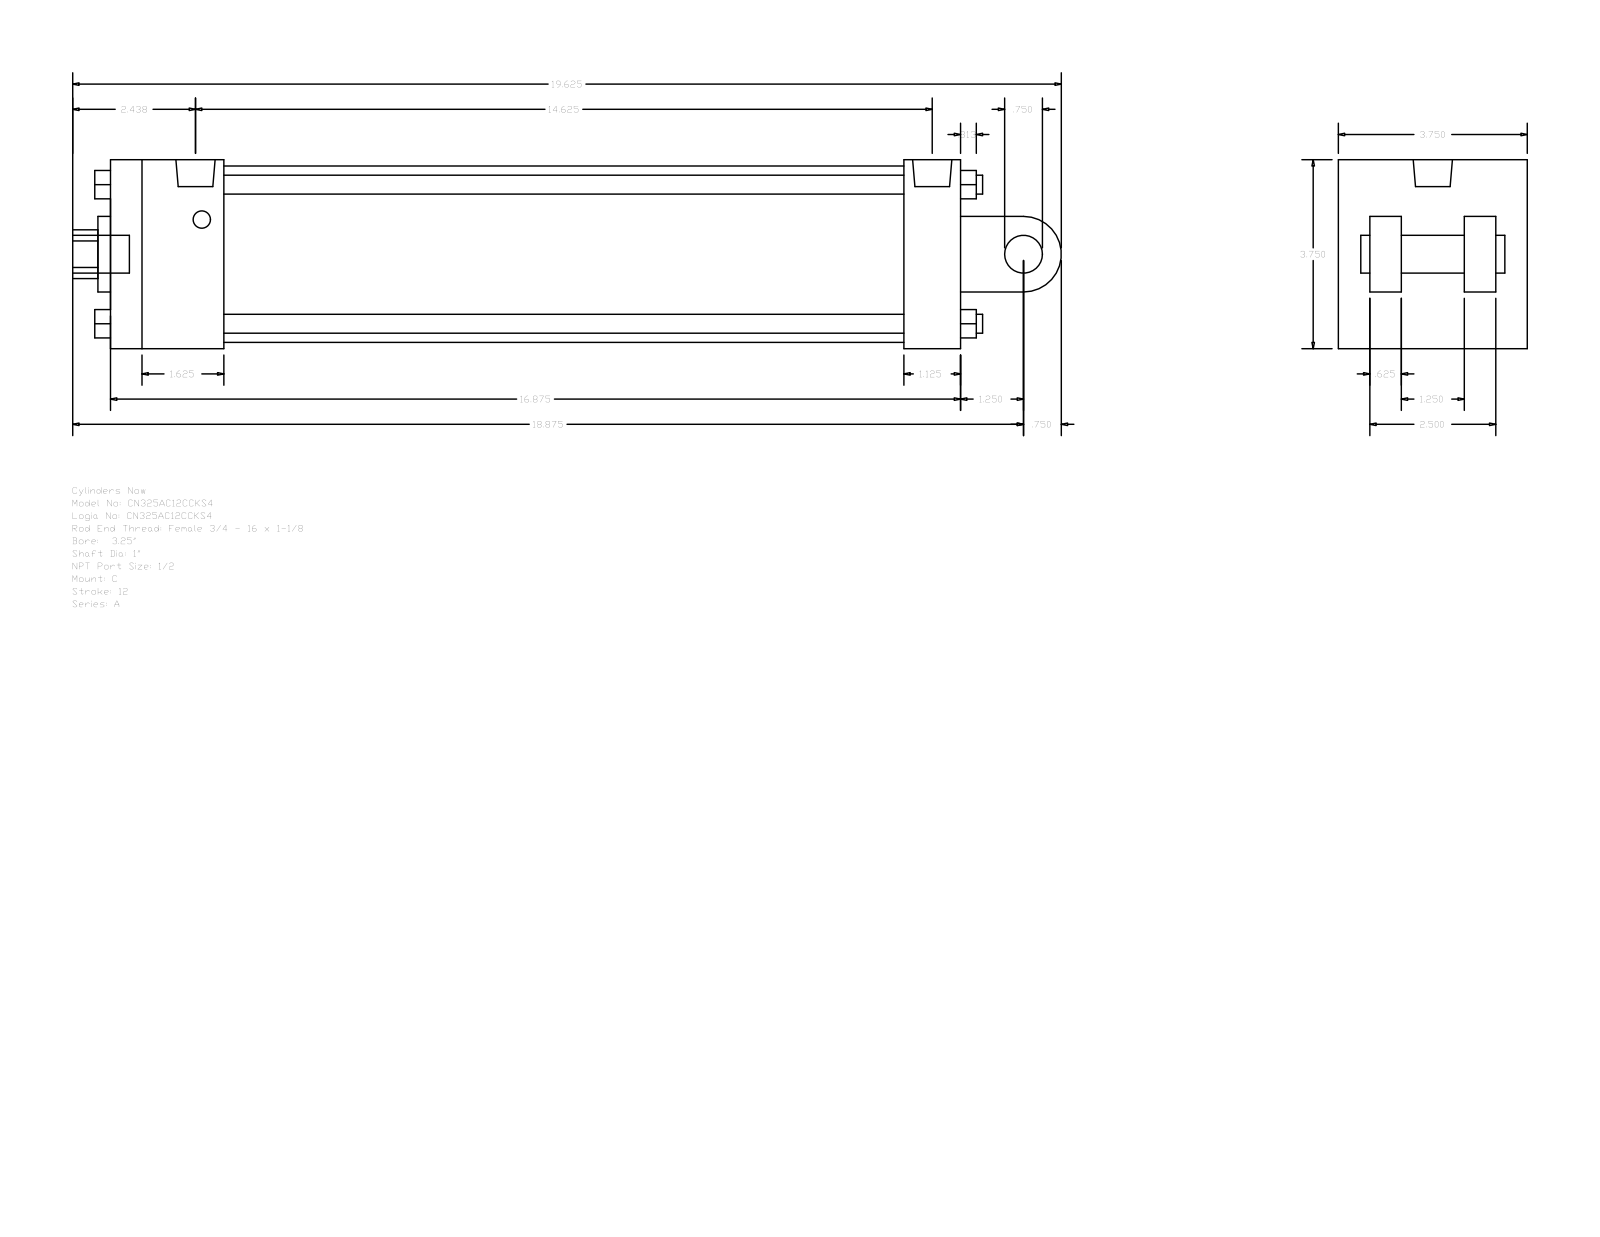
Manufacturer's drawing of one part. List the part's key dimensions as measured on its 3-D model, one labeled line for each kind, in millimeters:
Part name (STEP PRODUCT): A_C__0325_1
STEP written by: GSSL Pune (CONFIG_CONTROL_DESIGN)
Units: millimetres
Bodies: 0 solids, 135 faces (102 planar, 33 cylindrical, 0 other)
Overall size (bounding box): 498.48 × 95.25 × 95.25
Round holes (diameter × count): ⌀8.73 ×2, ⌀19.77 ×1, ⌀25.4 ×1, ⌀38.1 ×1, ⌀88.9 ×1
Round bosses / shafts (diameter × count): ⌀9.53 ×4, ⌀19.05 ×2, ⌀8.73 ×2, ⌀19.77 ×1
Partial cylindrical surfaces — rounded edges, fillets, slot ends (radius × count): R12.29 ×1, R19.05 ×1
Main face-to-face distances: 95.24, 428.63, 15.87, 63.5, 47.63, 79.37, 31.74, 66.67, 400.05, 28.58
Hole centre spacings: 3.18
